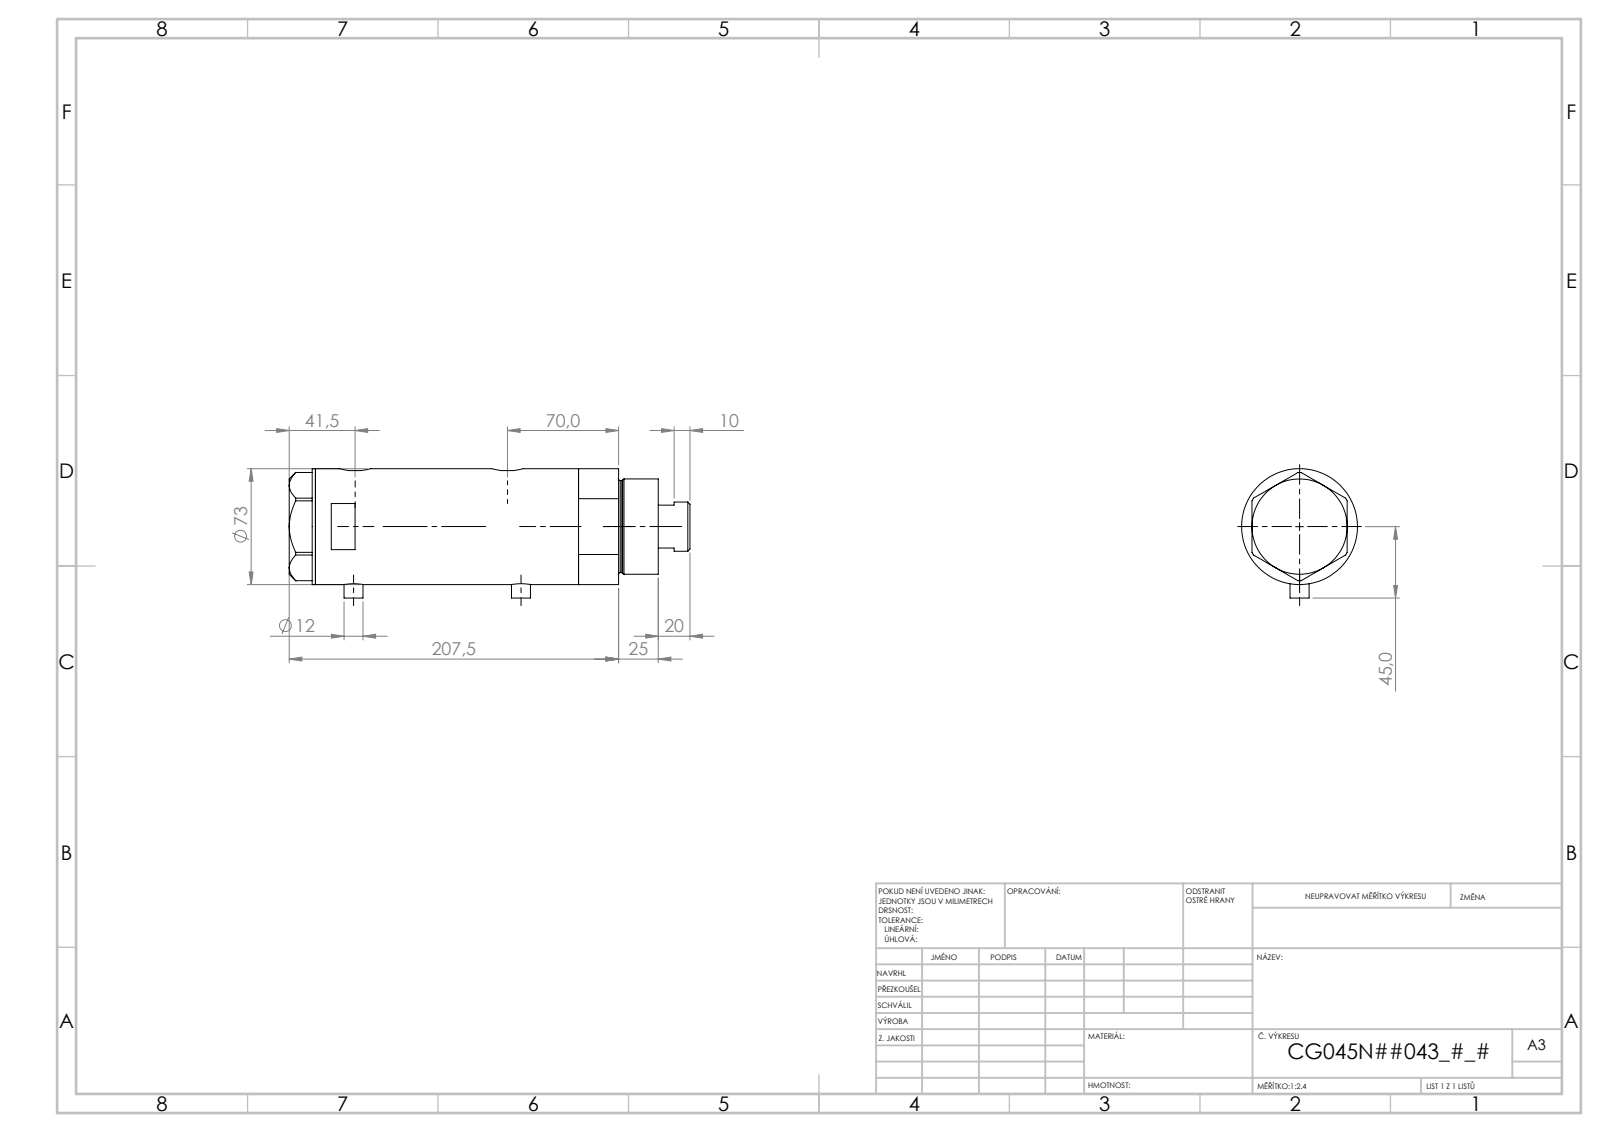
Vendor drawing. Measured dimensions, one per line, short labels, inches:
name: V270CG_FRONT; V270CG_MIDDLE; V270CG_BACK; V270CG_VC
written by: SolidWorks 2019 (CONFIG_CONTROL_DESIGN)
unit: in
bodies: 4 solids, 125 faces (50 planar, 55 cylindrical, 20 other)
size: 9.233 × 2.917 × 2.874
volume: 49.61 in³; area: 217.3 in²
holes: 2× ⌀0.197, 2× ⌀0.492, 2× ⌀0.518, 1× ⌀0.413, 1× ⌀1.26, 1× ⌀1.319, 1× ⌀1.772, 1× ⌀1.89, 1× ⌀2.52
bosses: 2× ⌀0.472, 1× ⌀2.874, 1× ⌀2.362, 1× ⌀2.283, 1× ⌀1.22
rounds: 2× R0.394
face distances: 4.336, 1.024, 3.313, 0.65, 1.673, 4.986, 7.796, 8.445, 6.772, 3.459
hole spacings: 3.726, 0.039, 0.039, 0.335, 0.335, 3.352, 3.391, 3.392
